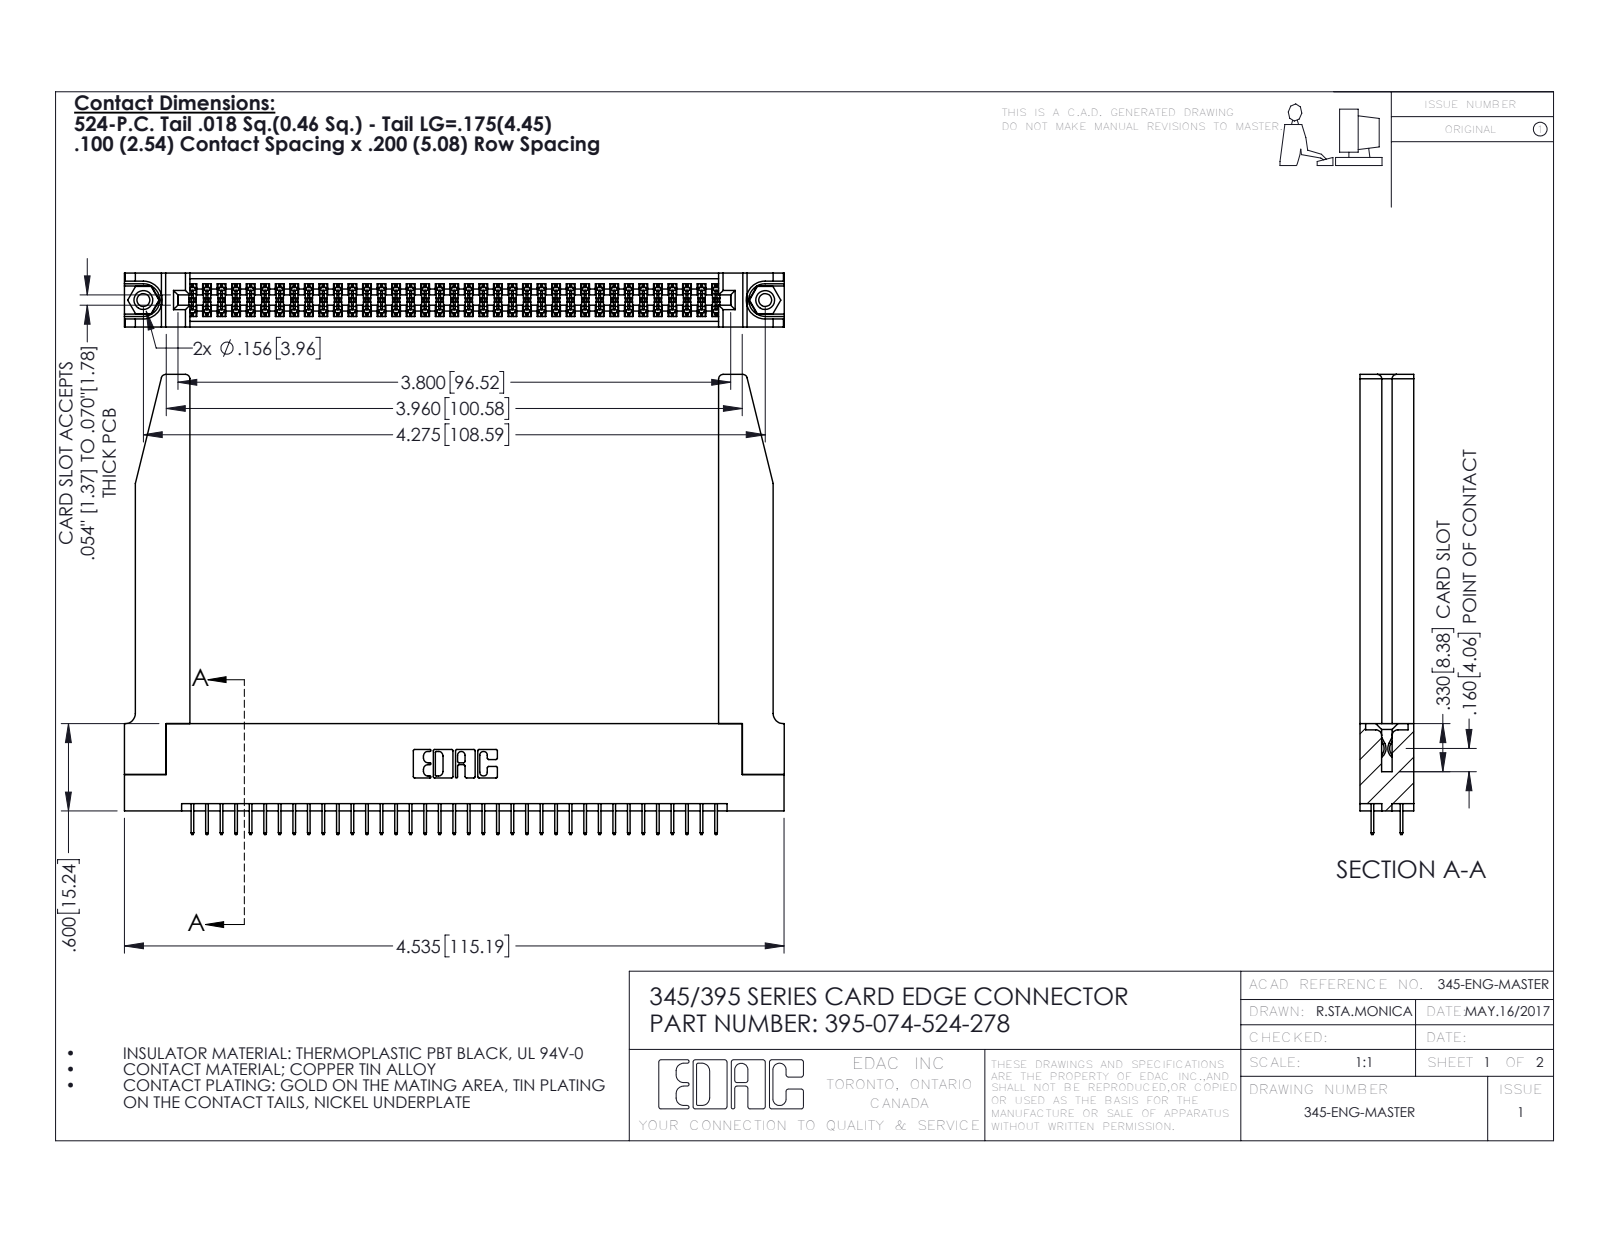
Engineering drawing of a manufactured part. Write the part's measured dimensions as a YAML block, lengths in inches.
part_name: "345-292-001_345-293-124; 345-250-001_345-250-001-102; 345-220-078_345-220-078; 395-074-524-278 (+1 more)"
step_written_by: "SolidWorks 2016 (CONFIG_CONTROL_DESIGN)"
units: inches
bodies: {solids: 79, faces: 4356, planar: 3108, cylindrical: 1196, other: 52}
overall_size: [4.536, 3.162, 0.37]
volume: 1.147
surface_area: 35.27
round_holes:
  - {diameter: 0.089, count: 2}
  - {diameter: 0.125, count: 2}
  - {diameter: 0.156, count: 2}
  - {diameter: 0.064, count: 1}
round_bosses_or_shafts:
  - {diameter: 0.155, count: 2}
partial_cylinders:
  - {radius: 0.006, count: 111}
  - {radius: 0.01, count: 22}
  - {radius: 0.03, count: 8}
  - {radius: 0.007, count: 6}
  - {radius: 0.031, count: 6}
  - {radius: 0.026, count: 3}
  - {radius: 0.014, count: 2}
  - {radius: 0.019, count: 2}
face_to_face_distances: [0.37, 0.072, 0.298, 0.2, 0.098, 0.272, 0.025, 0.225, 0.15, 0.148]
hole_center_spacings: [0.27, 4.039, 4.275]
